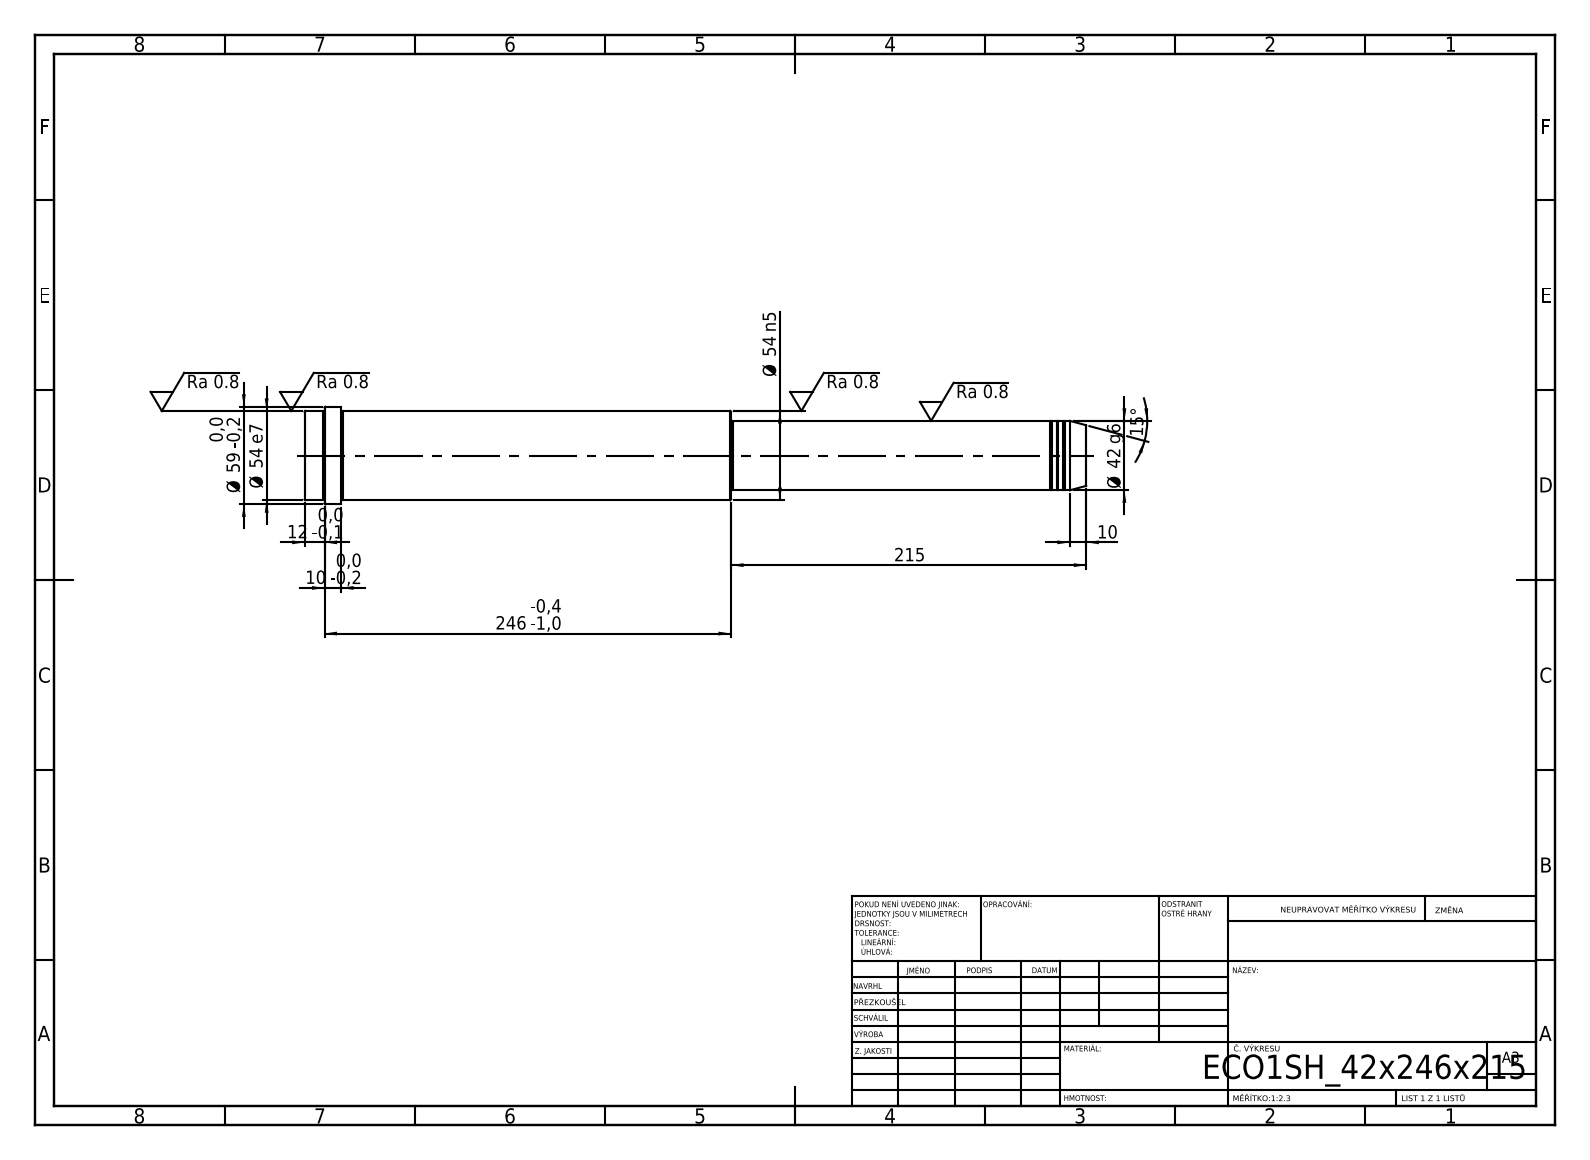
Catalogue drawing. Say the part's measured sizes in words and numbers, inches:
Its 3-D file was written by "SolidWorks 2019 (CONFIG_CONTROL_DESIGN)". It is 1 solid with 52 faces: 6 planar, 16 cylindrical and 30 other. Overall it measures 18.622 by 2.323 by 2.323 inches. Its volume is 54.38 cubic inches and its surface area 120.5 square inches. Round bosses or shafts: 1 of diameter 2.323, 1 of diameter 2.126, 1 of diameter 1.654, 1 of diameter 1.614. The main face-to-face distances are 18.622, 8.465, 10.157, 17.756, 9.291, 0.866, 18.15, 9.685, 0.394, 0.472.
